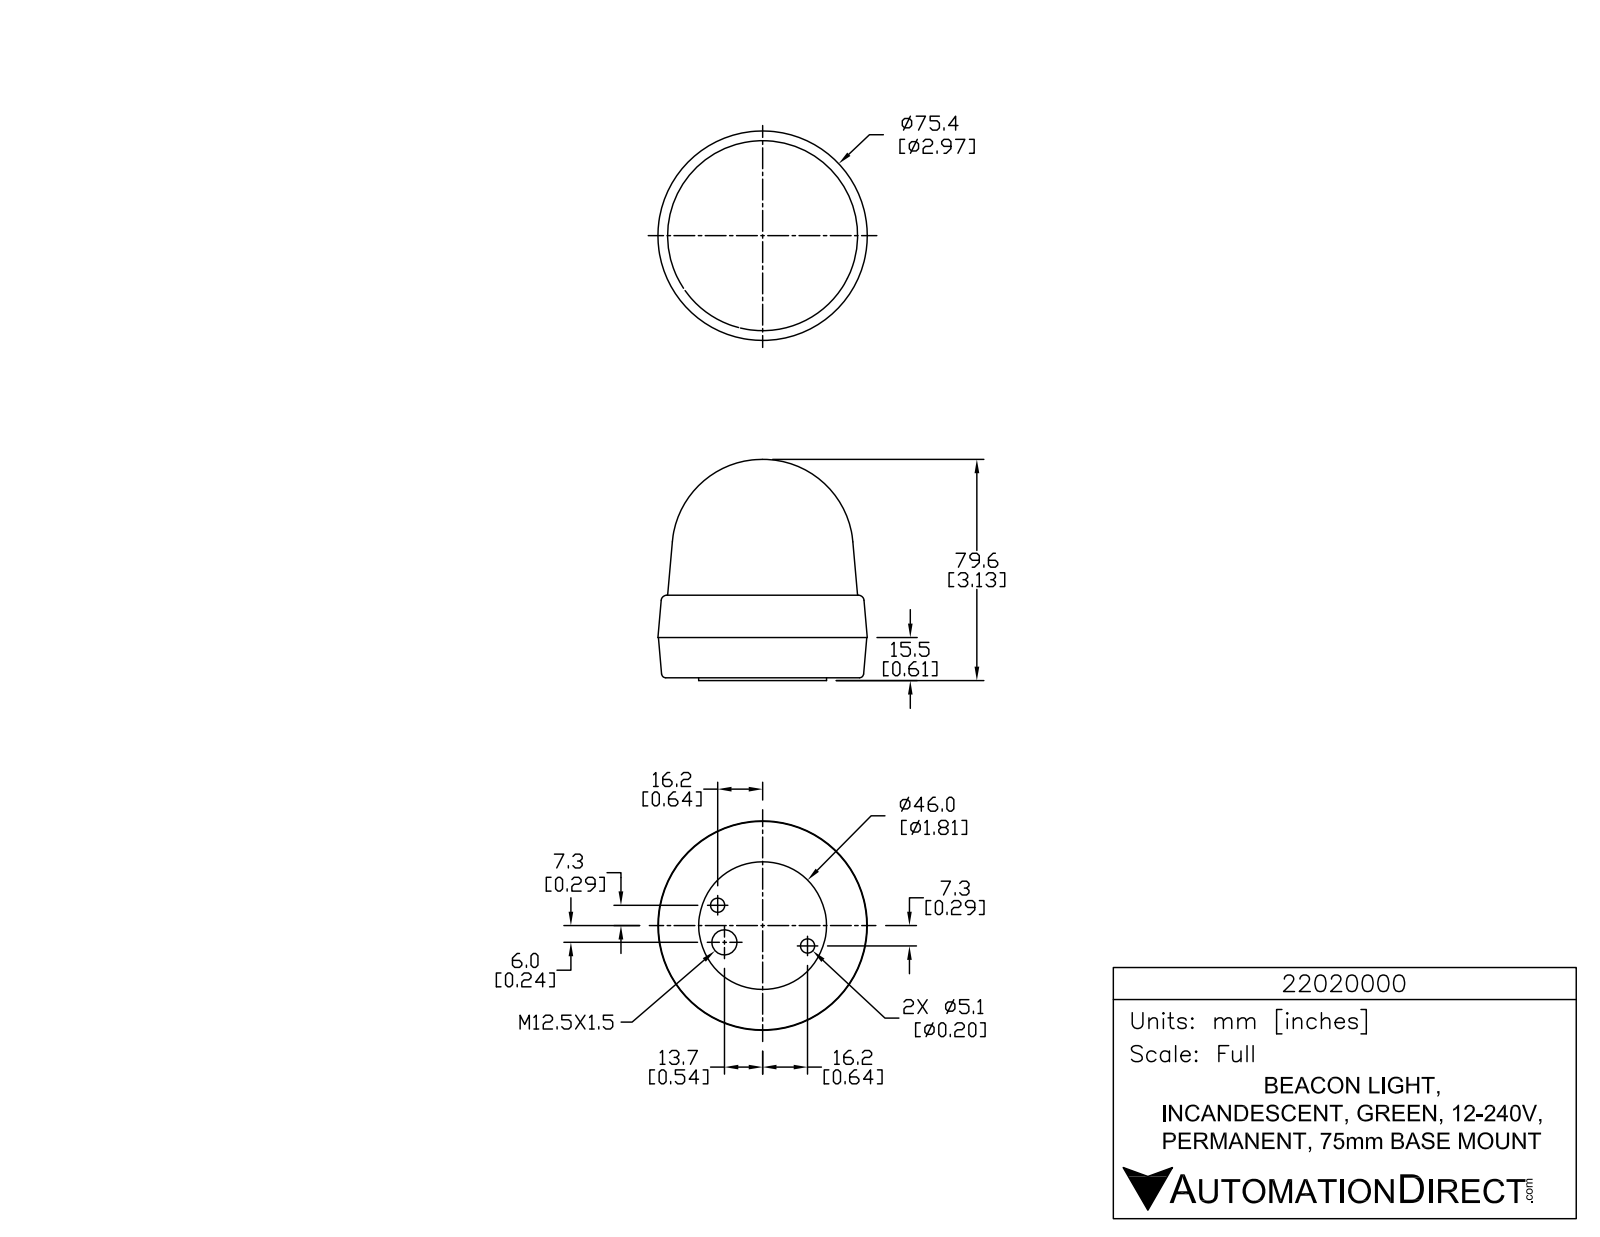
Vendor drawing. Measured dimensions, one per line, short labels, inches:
name: 22020000
written by: SolidWorks 2015 (AUTOMOTIVE_DESIGN)
unit: in
bodies: 1 solid, 773 faces (526 planar, 163 cylindrical, 84 other)
size: 3.133 × 2.967 × 2.967
volume: 15.79 in³; area: 33.7 in²
holes: 3× ⌀0.059, 2× ⌀0.201, 1× ⌀0.354
bosses: 3× ⌀0.339, 3× ⌀0.084, 1× ⌀1.811
rounds: 9× R0.005, 6× R0.005, 6× R0.012, 6× R0.012, 6× R0.012, 6× R0.196, 3× R0.005, 3× R0.005
face distances: 0.039, 1.209, 1.17, 0.61, 0.571, 0.599, 1.566, 1.527, 0.956, 0.357
hole spacings: 0.534, 1.179, 1.398
